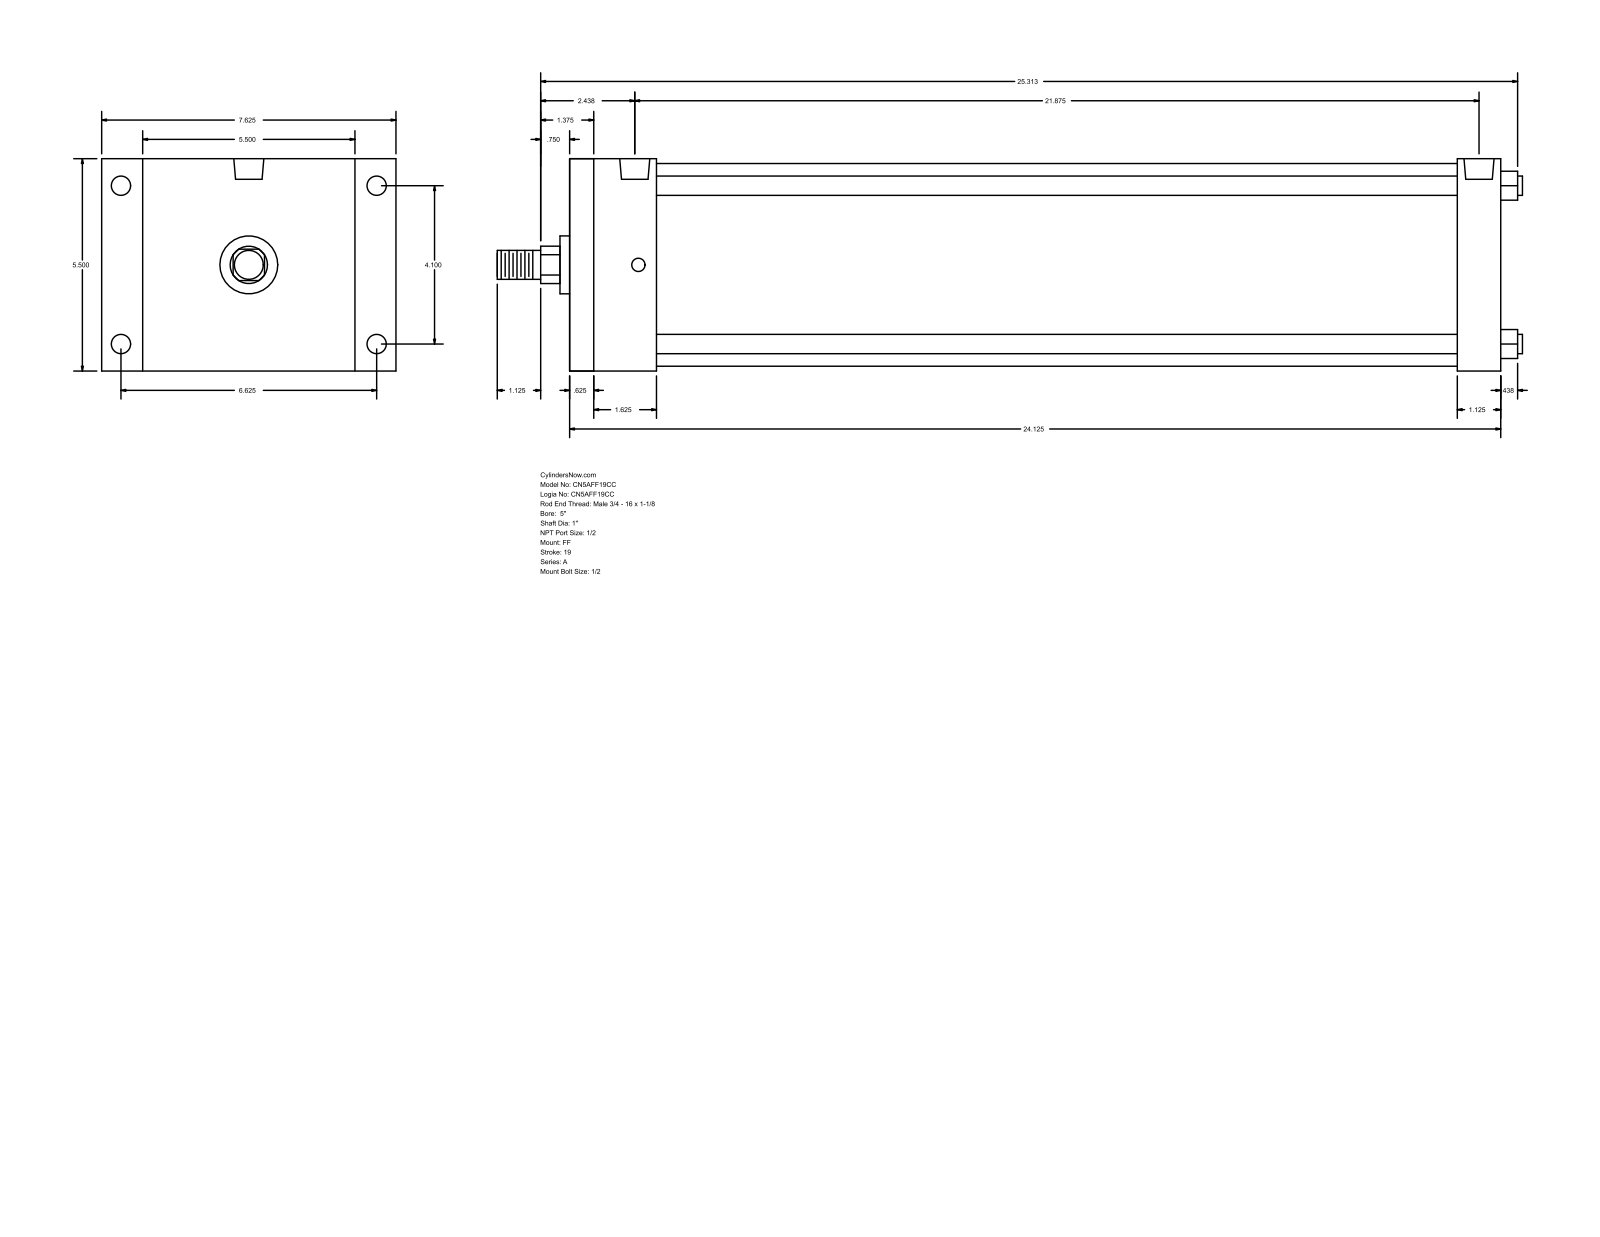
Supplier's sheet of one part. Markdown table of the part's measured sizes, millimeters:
| quantity | value |
| --- | --- |
| part name | A_FF__0500_1 |
| STEP written by | GSSL Pune (CONFIG_CONTROL_DESIGN) |
| units | millimeters |
| bodies | 0 solids, 92 faces (64 planar, 28 cylindrical, 0 other) |
| overall size | 674.69 × 193.68 × 139.7 |
| round holes (diameter × count) | 8.73 × 4, 12.7 × 4, 19.77 × 2 |
| round bosses / shafts (diameter × count) | 12.7 × 4, 133.35 × 1, 38.1 × 1, 25.4 × 1, 19.05 × 1 |
| partial cylindrical surfaces (radius × count) | 12.29 × 1 |
| main face-to-face distances | 139.7, 612.78, 15.87, 596.91, 584.2, 568.33, 28.58, 57.15, 41.28, 527.05 |
| hole center spacings | 2.39, 104.14, 168.28, 197.9, 550.85, 553.24, 555.63 |
